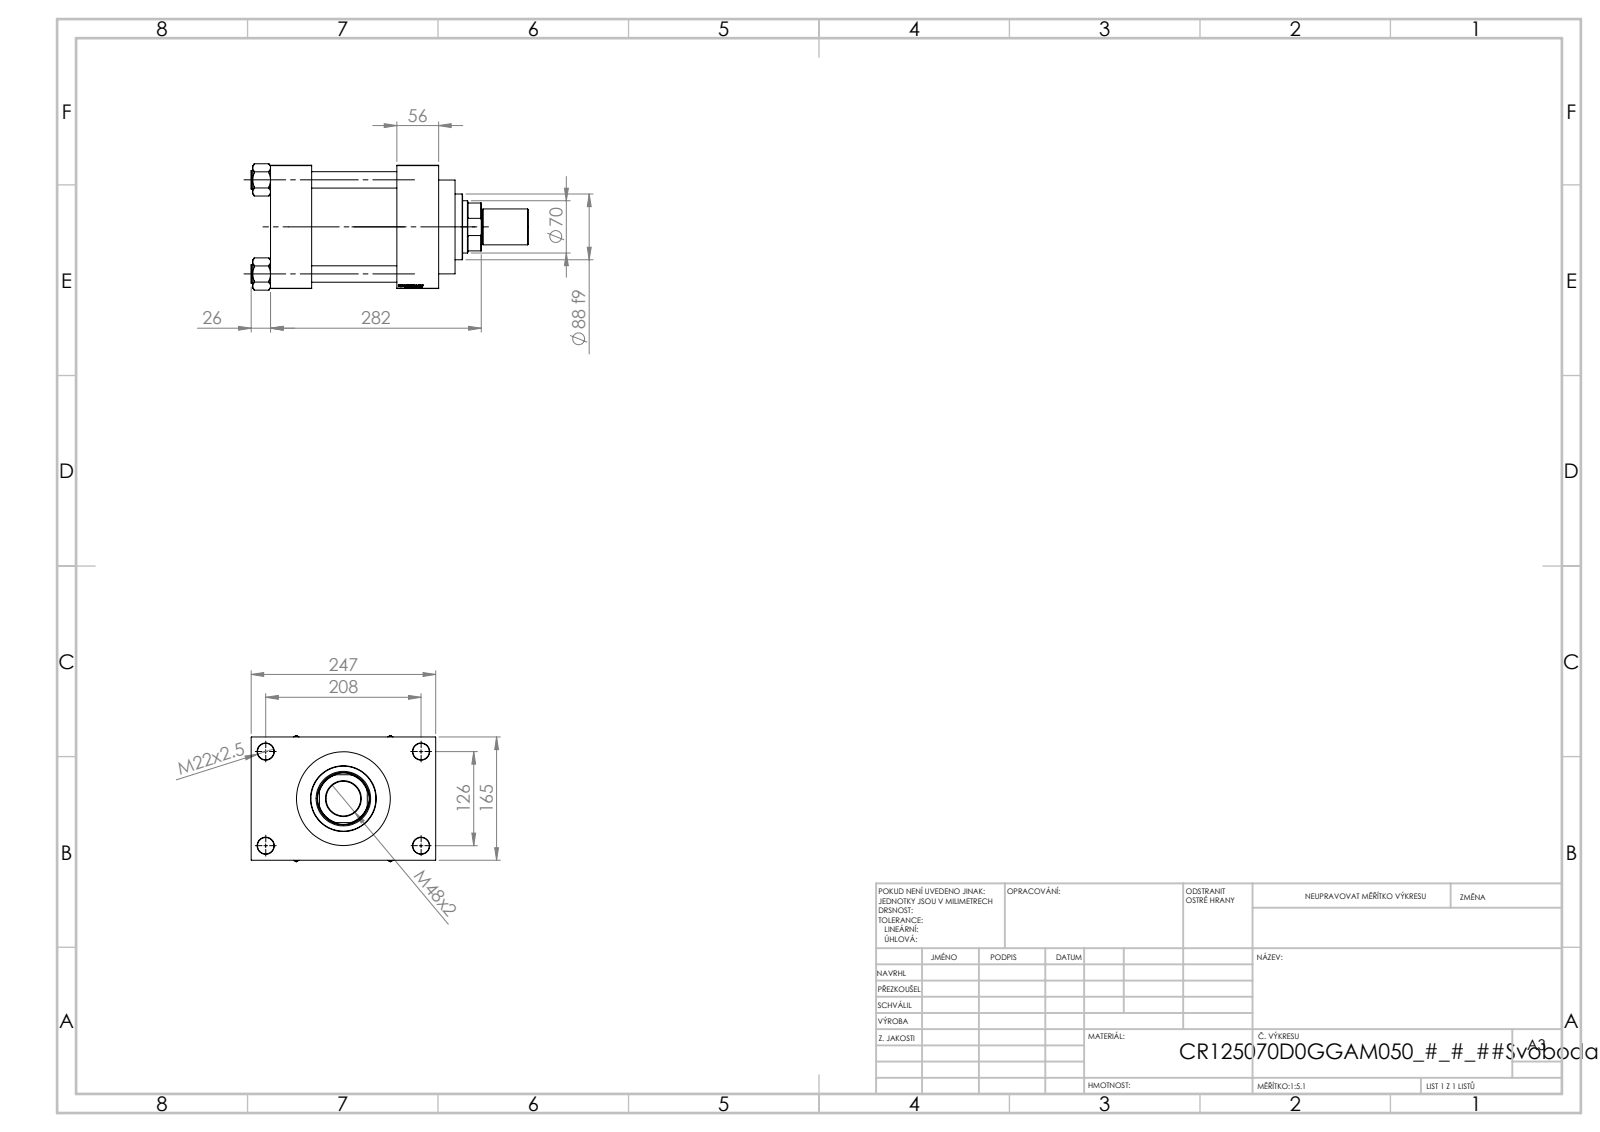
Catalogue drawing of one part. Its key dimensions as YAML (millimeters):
part_name: "V215CR_D_Body; V215CR_VCP_D; V215CR_D_TYCINKA; ROD_END_AH (+2 more)"
step_written_by: "SolidWorks 2019 (CONFIG_CONTROL_DESIGN)"
units: millimeters
bodies: {solids: 12, faces: 1163, planar: 548, cylindrical: 91, other: 524}
overall_size: [371, 247, 169.14]
volume: 5357000
surface_area: 590275
round_holes:
  - {diameter: 22, count: 8}
  - {diameter: 7, count: 2}
  - {diameter: 32.24, count: 2}
  - {diameter: 45, count: 2}
  - {diameter: 46.5, count: 1}
  - {diameter: 70, count: 1}
  - {diameter: 73, count: 1}
  - {diameter: 96, count: 1}
  - {diameter: 125, count: 1}
  - {diameter: 125.5, count: 1}
round_bosses_or_shafts:
  - {diameter: 25, count: 4}
  - {diameter: 131, count: 1}
  - {diameter: 88, count: 1}
  - {diameter: 48, count: 1}
  - {diameter: 46, count: 1}
partial_cylinders:
  - {radius: 34, count: 1}
face_to_face_distances: [114, 165, 55, 169, 225, 170, 56, 41, 206, 247]
hole_center_spacings: [41.05, 89.02, 121.59, 125.9, 132.47, 166.95, 209.13, 126]
